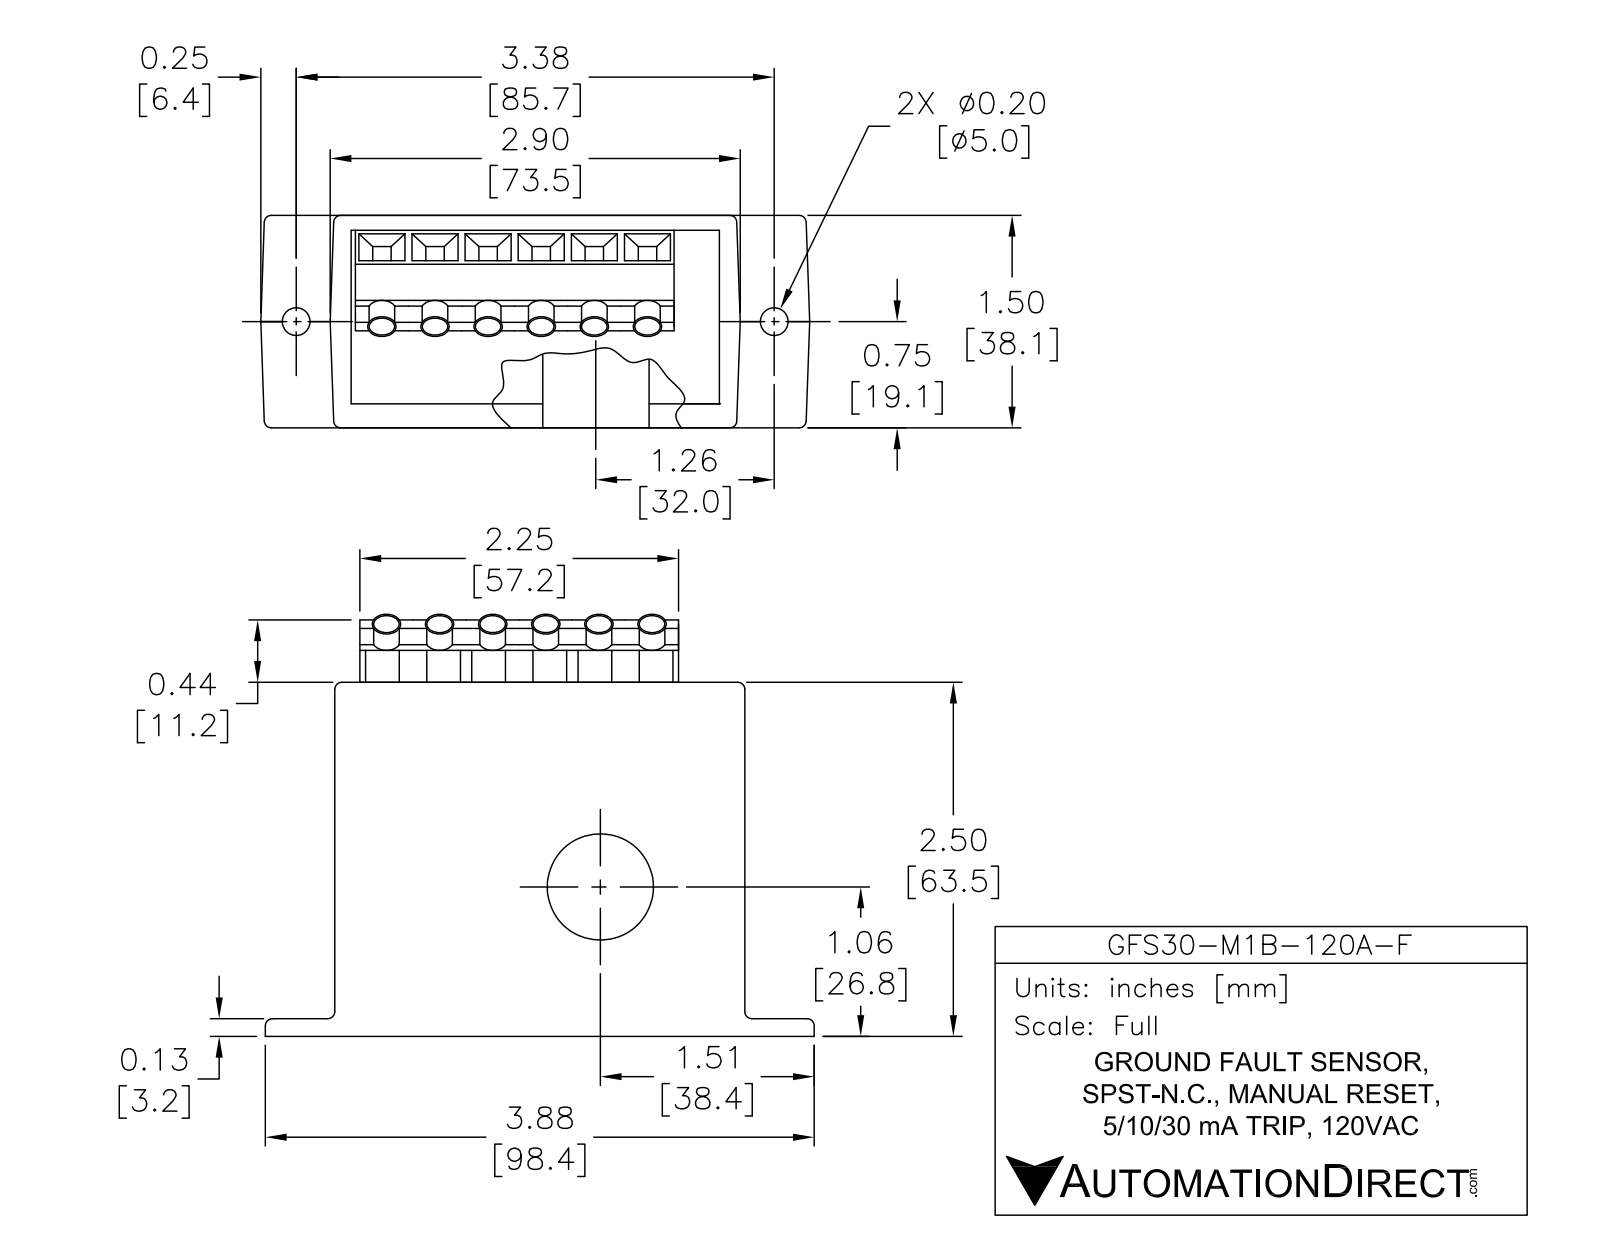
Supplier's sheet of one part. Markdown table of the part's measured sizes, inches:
| quantity | value |
| --- | --- |
| part name | GFS30-M1B-120A-F |
| STEP written by | SolidWorks 2019 (AUTOMOTIVE_DESIGN) |
| units | inches |
| bodies | 19 solids, 312 faces (252 planar, 56 cylindrical, 4 other) |
| overall size | 3.875 × 2.908 × 1.504 |
| volume | 10.56 in³ |
| surface area | 54.48 in² |
| round holes (diameter × count) | 0.206 × 6, 0.196 × 2, 0.2 × 2, 0.75 × 1 |
| round bosses / shafts (diameter × count) | 0.186 × 6 |
| partial cylindrical surfaces (radius × count) | 0.128 × 6 |
| main face-to-face distances | 1.5, 2.895, 0.1, 2.455, 2.355, 1.504, 0.104, 2.459, 0.045, 2.334 |
| hole center spacings | 0.748, 0.354, 0.394, 0.37, 0.374, 0.681, 0.768, 1.022 |
